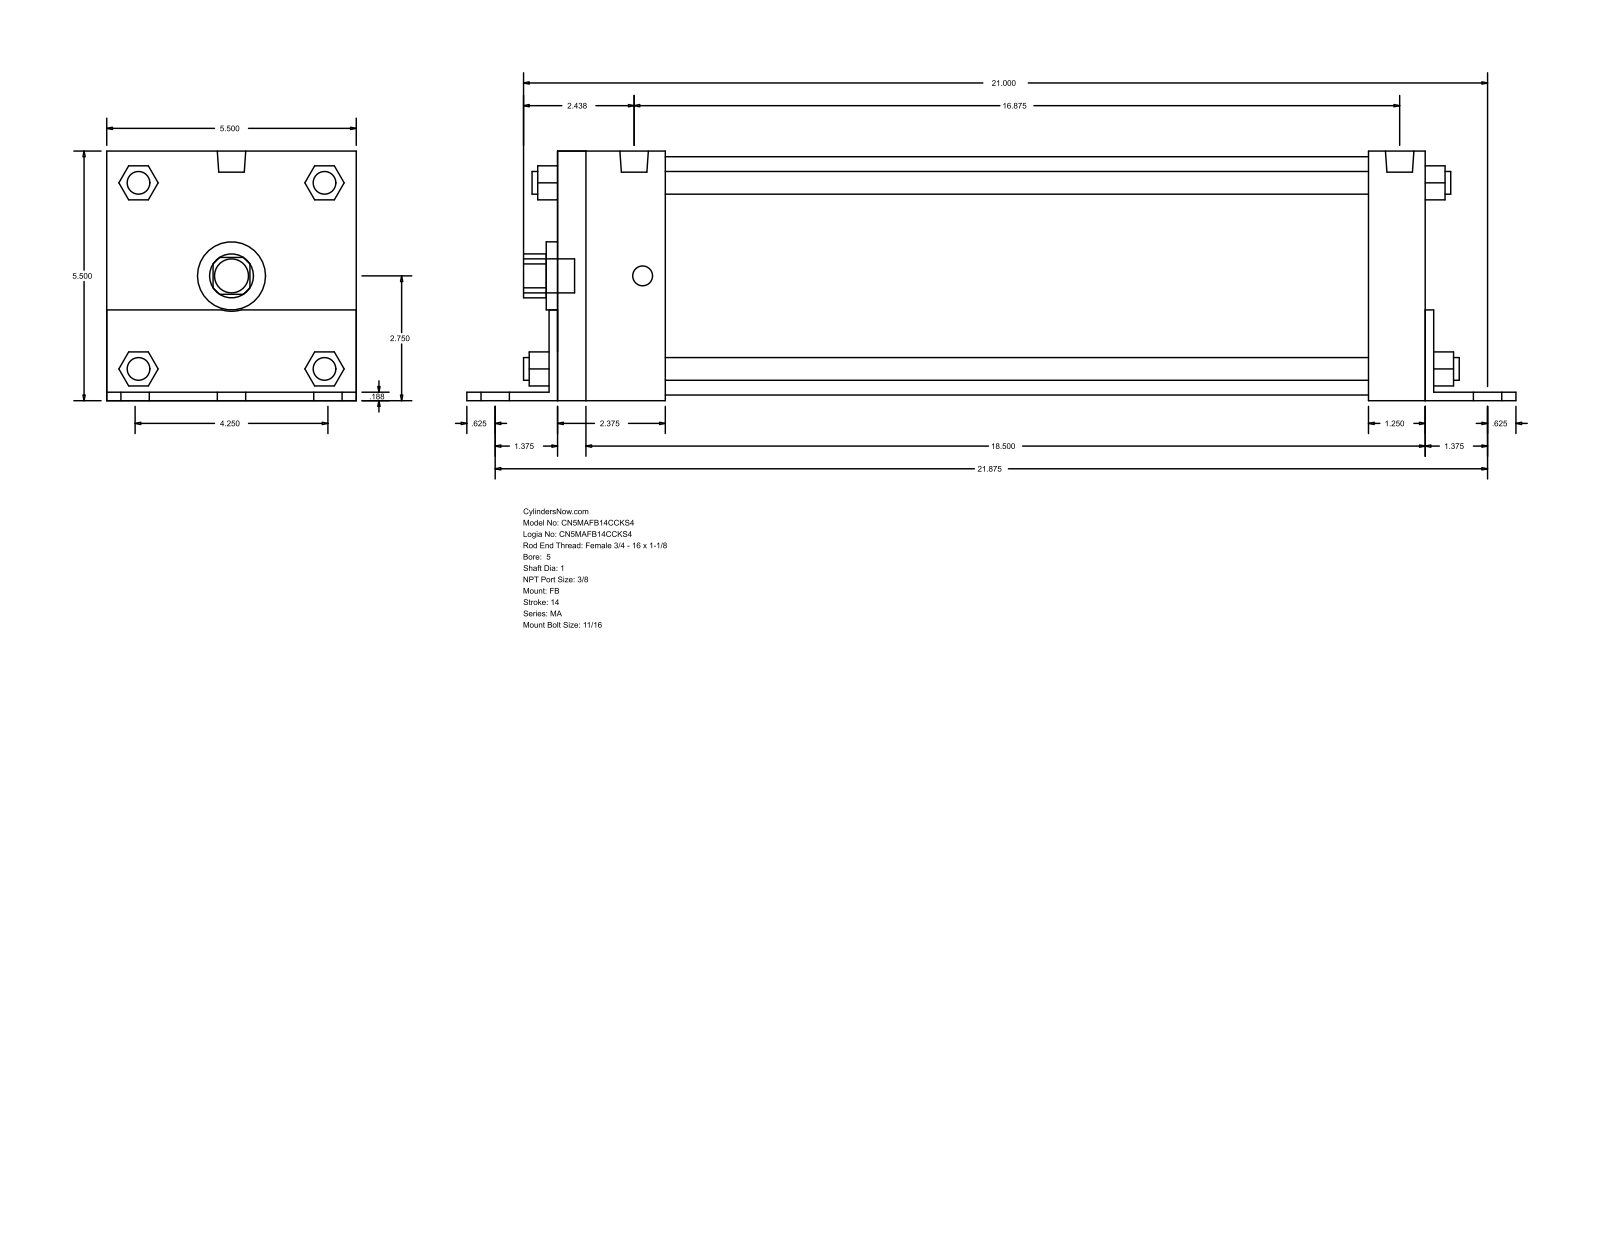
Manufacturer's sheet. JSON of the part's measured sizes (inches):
{"part_name": "MA_FB__0500_1", "step_written_by": "GSSL Pune (CONFIG_CONTROL_DESIGN)", "units": "inches", "bodies": {"solids": 0, "faces": 140, "planar": 105, "cylindrical": 35, "other": 0}, "overall_size": [23.125, 5.502, 5.5], "round_holes": [[1, 1], [1.5, 1], [5.25, 1]], "round_bosses_or_shafts": [[0.687, 6], [0.5, 4], [0.437, 4], [0.627, 2], [0.75, 1]], "partial_cylinders_radius": [[0.484, 1], [0.78, 1]], "face_to_face_distances": [5.5, 0.187, 5.502, 0.185, 5.315, 19.125, 0.188, 19.313, 19.312, 19.5]}
